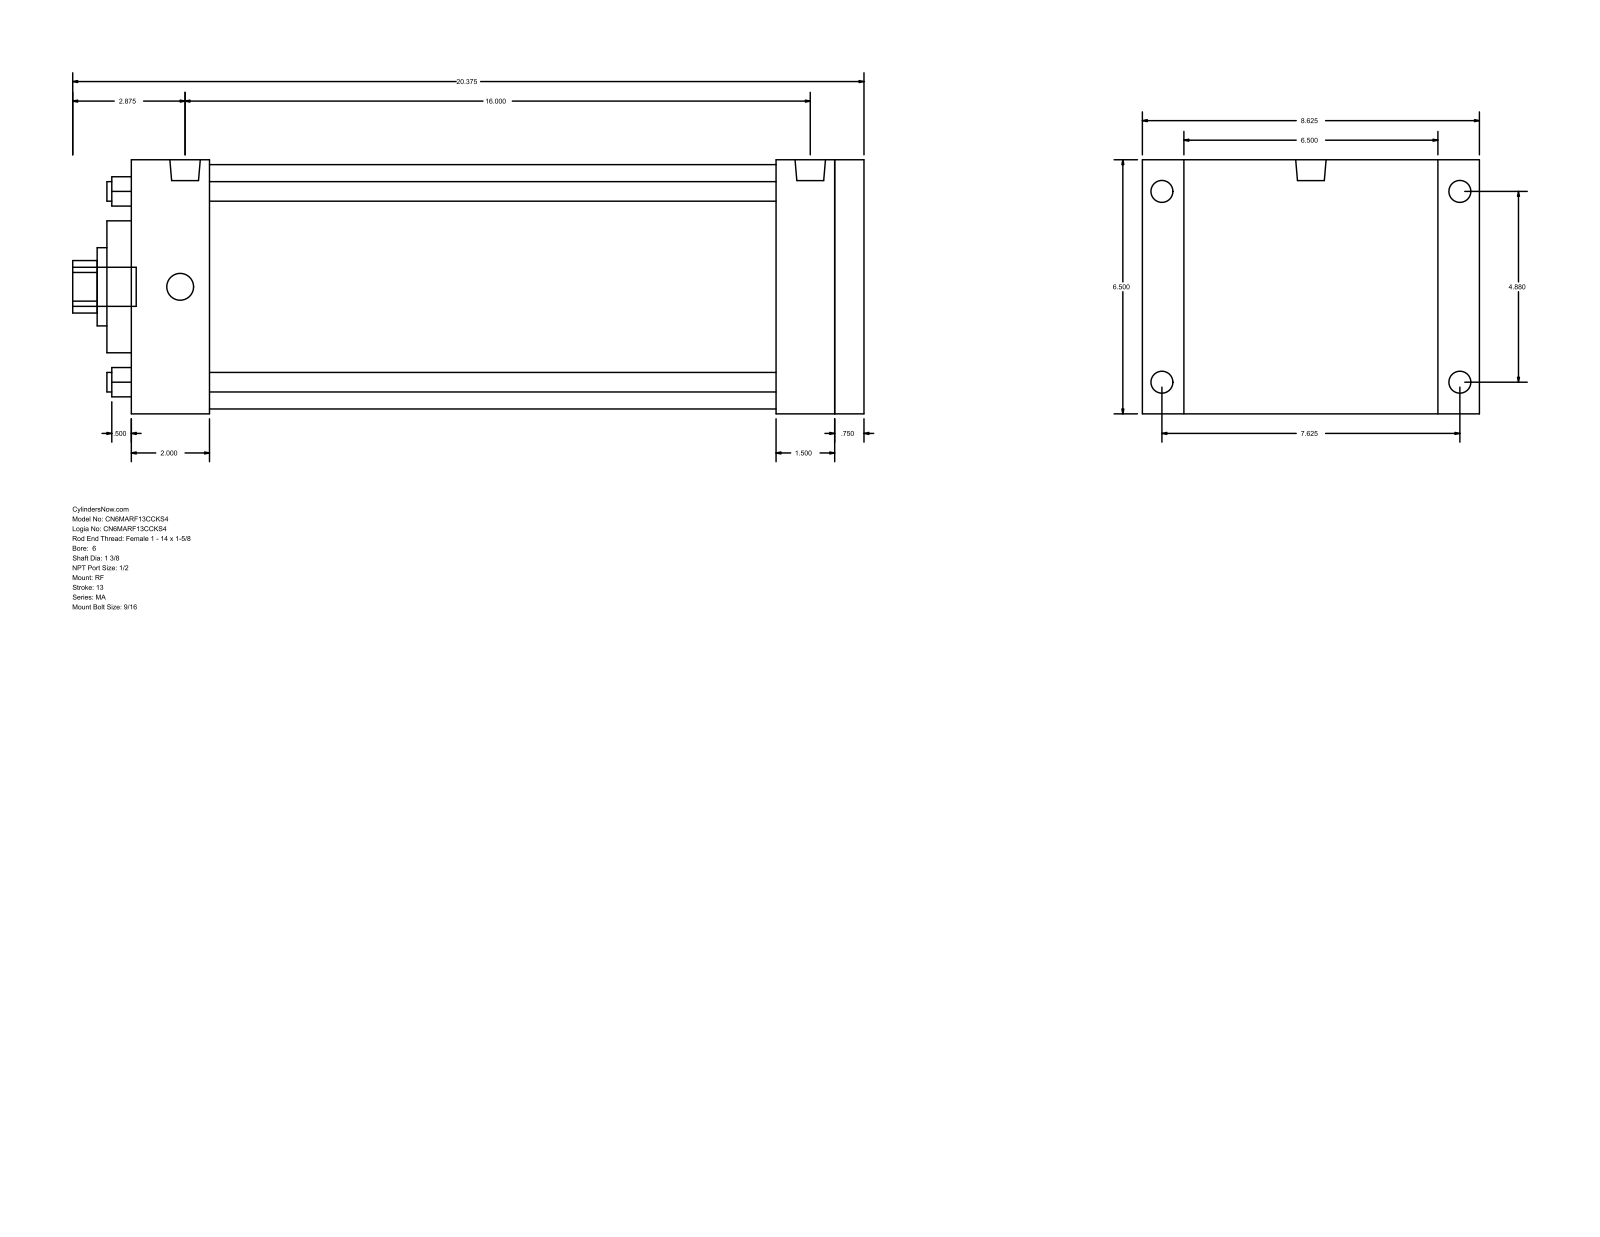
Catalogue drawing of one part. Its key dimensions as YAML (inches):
part_name: "MA_RF__0600_1.375"
step_written_by: "GSSL Pune (CONFIG_CONTROL_DESIGN)"
units: inches
bodies: {solids: 0, faces: 94, planar: 65, cylindrical: 29, other: 0}
overall_size: [20.375, 8.625, 6.5]
round_holes:
  - {diameter: 0.5, count: 4}
  - {diameter: 1.375, count: 1}
  - {diameter: 2, count: 1}
  - {diameter: 3.375, count: 1}
  - {diameter: 6.25, count: 1}
round_bosses_or_shafts:
  - {diameter: 0.687, count: 4}
  - {diameter: 0.563, count: 4}
  - {diameter: 0.778, count: 2}
  - {diameter: 1, count: 1}
partial_cylinders:
  - {radius: 0.672, count: 1}
face_to_face_distances: [6.5, 18.875, 0.75, 18.125, 1.5, 2, 16.125, 16.875, 16.625, 14.625]
hole_center_spacings: [3.451, 4.88, 6.902]
